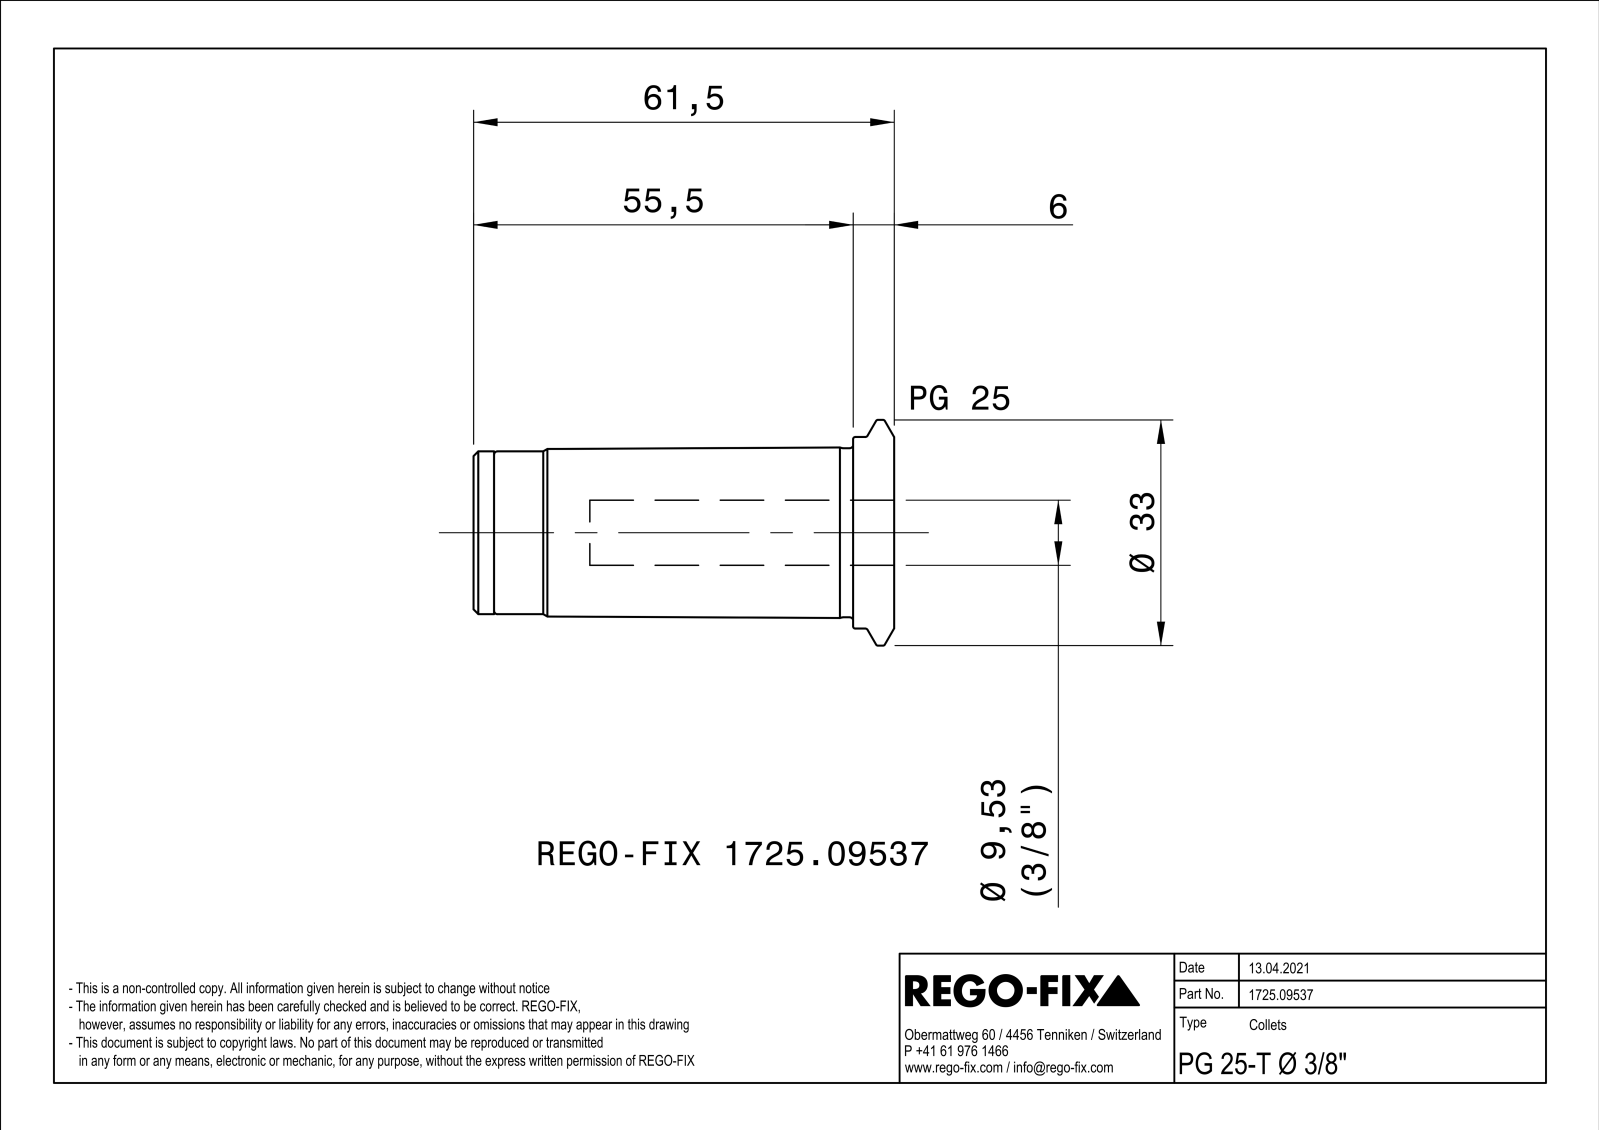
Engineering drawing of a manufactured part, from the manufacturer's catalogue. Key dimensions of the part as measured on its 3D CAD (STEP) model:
Part name (STEP PRODUCT): NOCUT
STEP written by: SIEMENS PLM Software Solid Edge ST10 (AUTOMOTIVE_DESIGN)
Units: millimetres
Bodies: 0 solids, 86 faces (24 planar, 22 cylindrical, 40 other)
Overall size (bounding box): 58.5 × 33 × 32.94
Round holes (diameter × count): ⌀3.24 ×1, ⌀4.3 ×1, ⌀9.53 ×1, ⌀21 ×1, ⌀22 ×1
Round bosses / shafts (diameter × count): ⌀33 ×1, ⌀28 ×1, ⌀24.7 ×1, ⌀23.8 ×1
Partial cylindrical surfaces — rounded edges, fillets, slot ends (radius × count): R0.5 ×2, R4.06 ×1, R4.17 ×1
Main face-to-face distances: 1, 6, 55.9, 57, 49.9, 51, 1.1, 58.5, 52.5, 2.6
